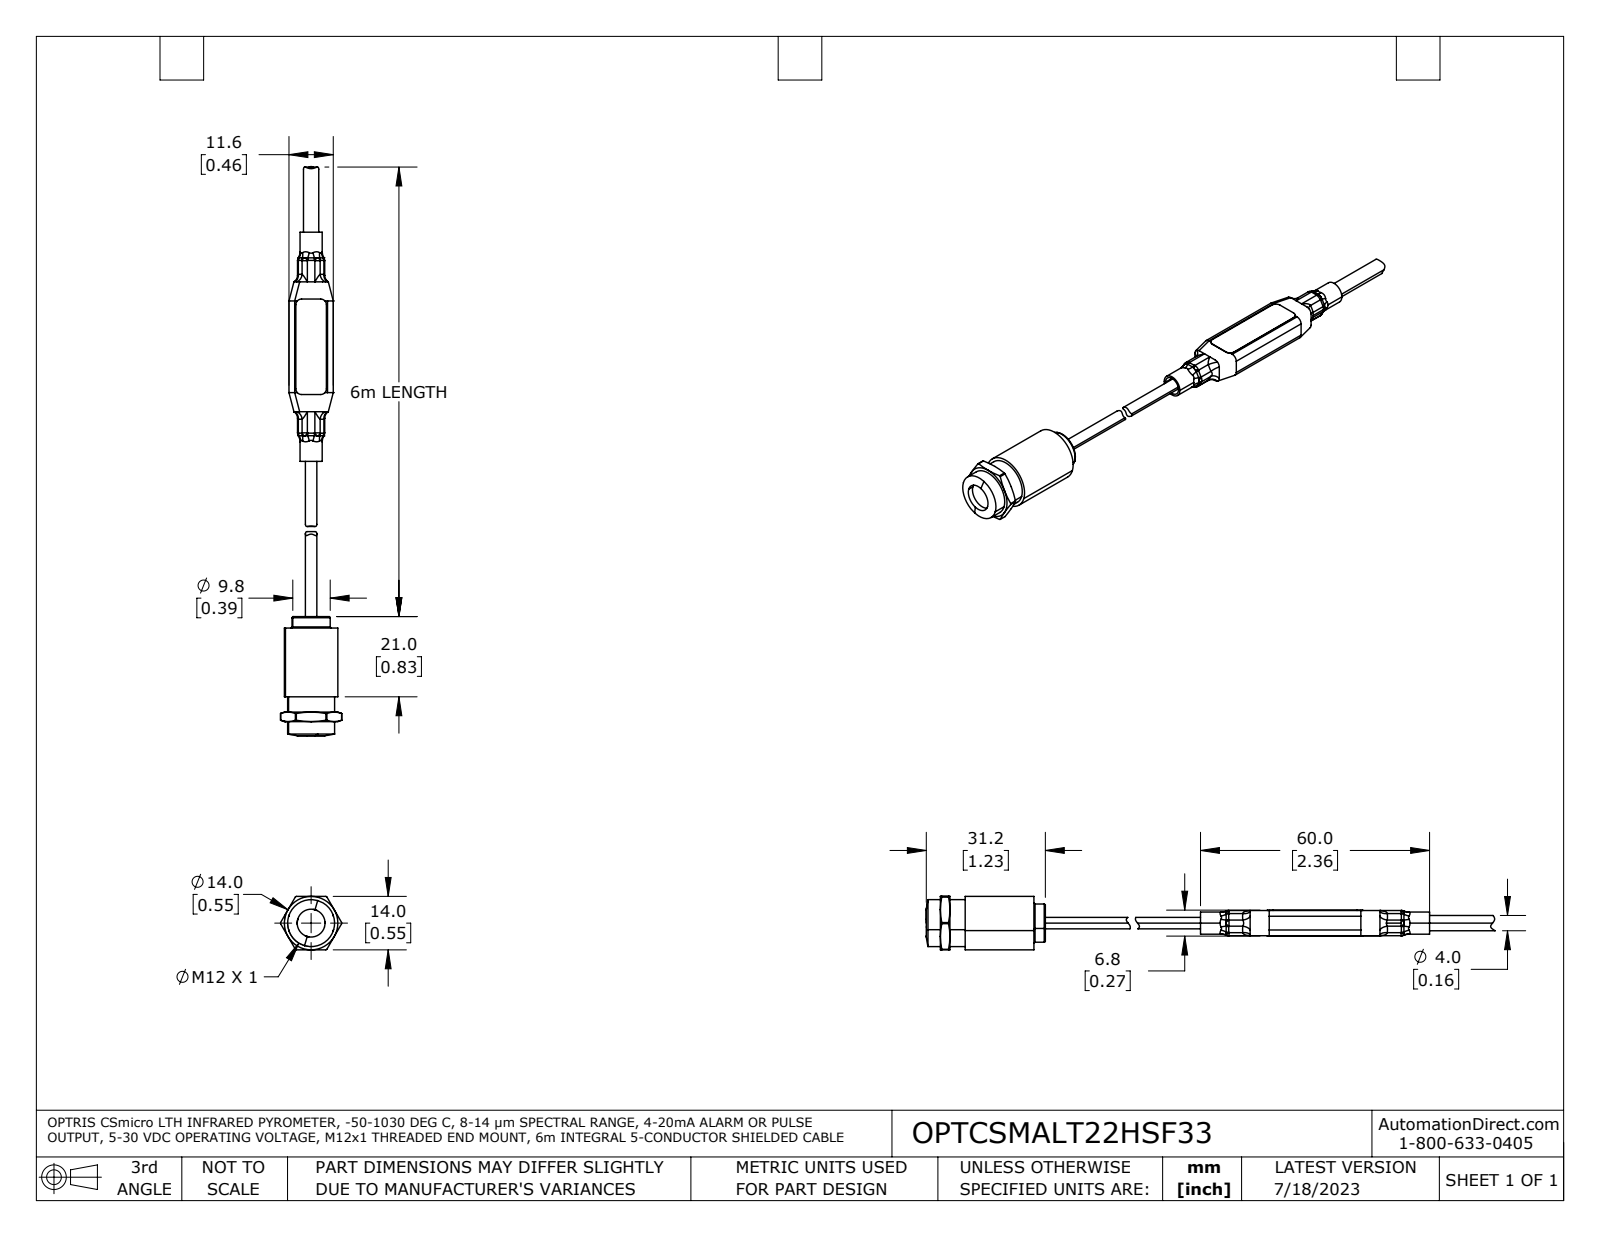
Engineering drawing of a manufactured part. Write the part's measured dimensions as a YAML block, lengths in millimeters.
part_name: "Sensing-head-CSmicro-28mm nc ext2 sr1-srf coord fxt comb1 sr1 fxt"
step_written_by: "SolidWorks 2021 (AUTOMOTIVE_DESIGN)"
units: millimeters
bodies: {solids: 10, faces: 545, planar: 86, cylindrical: 174, other: 285}
overall_size: [149, 16, 14]
volume: 6260
surface_area: 7523
round_holes:
  - {diameter: 1.2, count: 2}
  - {diameter: 3, count: 1}
  - {diameter: 3.2, count: 1}
  - {diameter: 4.6, count: 1}
  - {diameter: 4.8, count: 1}
  - {diameter: 7.3, count: 1}
round_bosses_or_shafts:
  - {diameter: 0.8, count: 10}
  - {diameter: 0.9, count: 8}
  - {diameter: 0.5, count: 8}
  - {diameter: 14, count: 1}
  - {diameter: 12.3, count: 1}
  - {diameter: 10, count: 1}
  - {diameter: 5.8, count: 1}
  - {diameter: 5.2, count: 1}
partial_cylinders:
  - {radius: 1.5, count: 8}
  - {radius: 1.1, count: 6}
  - {radius: 1.6, count: 6}
  - {radius: 1, count: 4}
  - {radius: 0.4, count: 2}
  - {radius: 1.2, count: 1}
  - {radius: 8, count: 1}
face_to_face_distances: [0.5, 6.1, 6.6, 0.6, 6.2, 6.7, 5.6, 6.8, 11.1, 9.8]
hole_center_spacings: [4, 8]
